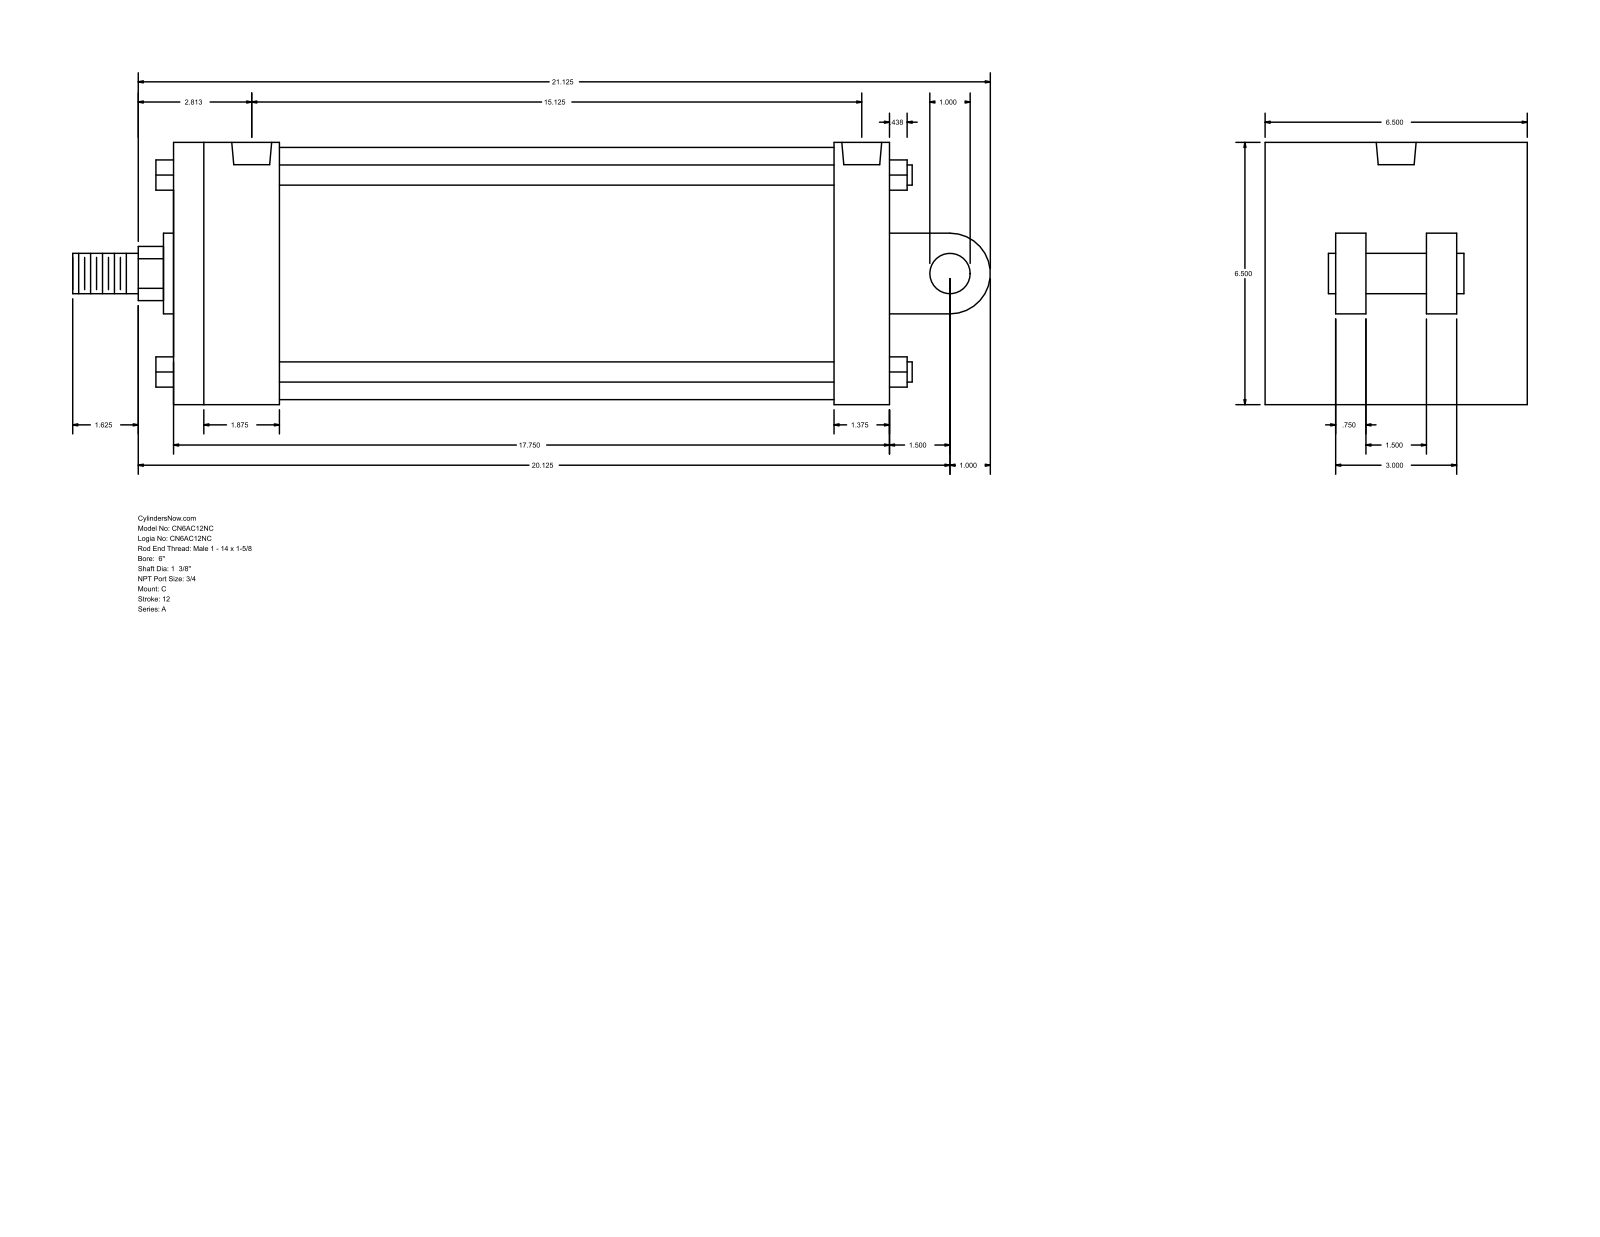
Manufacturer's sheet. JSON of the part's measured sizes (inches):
{"part_name": "A_C__0600_1.375", "step_written_by": "GSSL Pune (CONFIG_CONTROL_DESIGN)", "units": "inches", "bodies": {"solids": 0, "faces": 135, "planar": 102, "cylindrical": 33, "other": 0}, "overall_size": [22.75, 6.5, 6.5], "round_holes": [[0.594, 4], [0.989, 2]], "round_bosses_or_shafts": [[0.5, 4], [1, 2], [6.25, 1], [2, 1], [1.375, 1]], "partial_cylinders_radius": [[0.672, 1], [1, 1]], "face_to_face_distances": [6.5, 17.75, 2.25, 0.75, 2.625, 15.125, 16.375, 13.75, 1.375, 2.5], "hole_center_spacings": [0.219, 14.687, 14.906, 15.125]}
